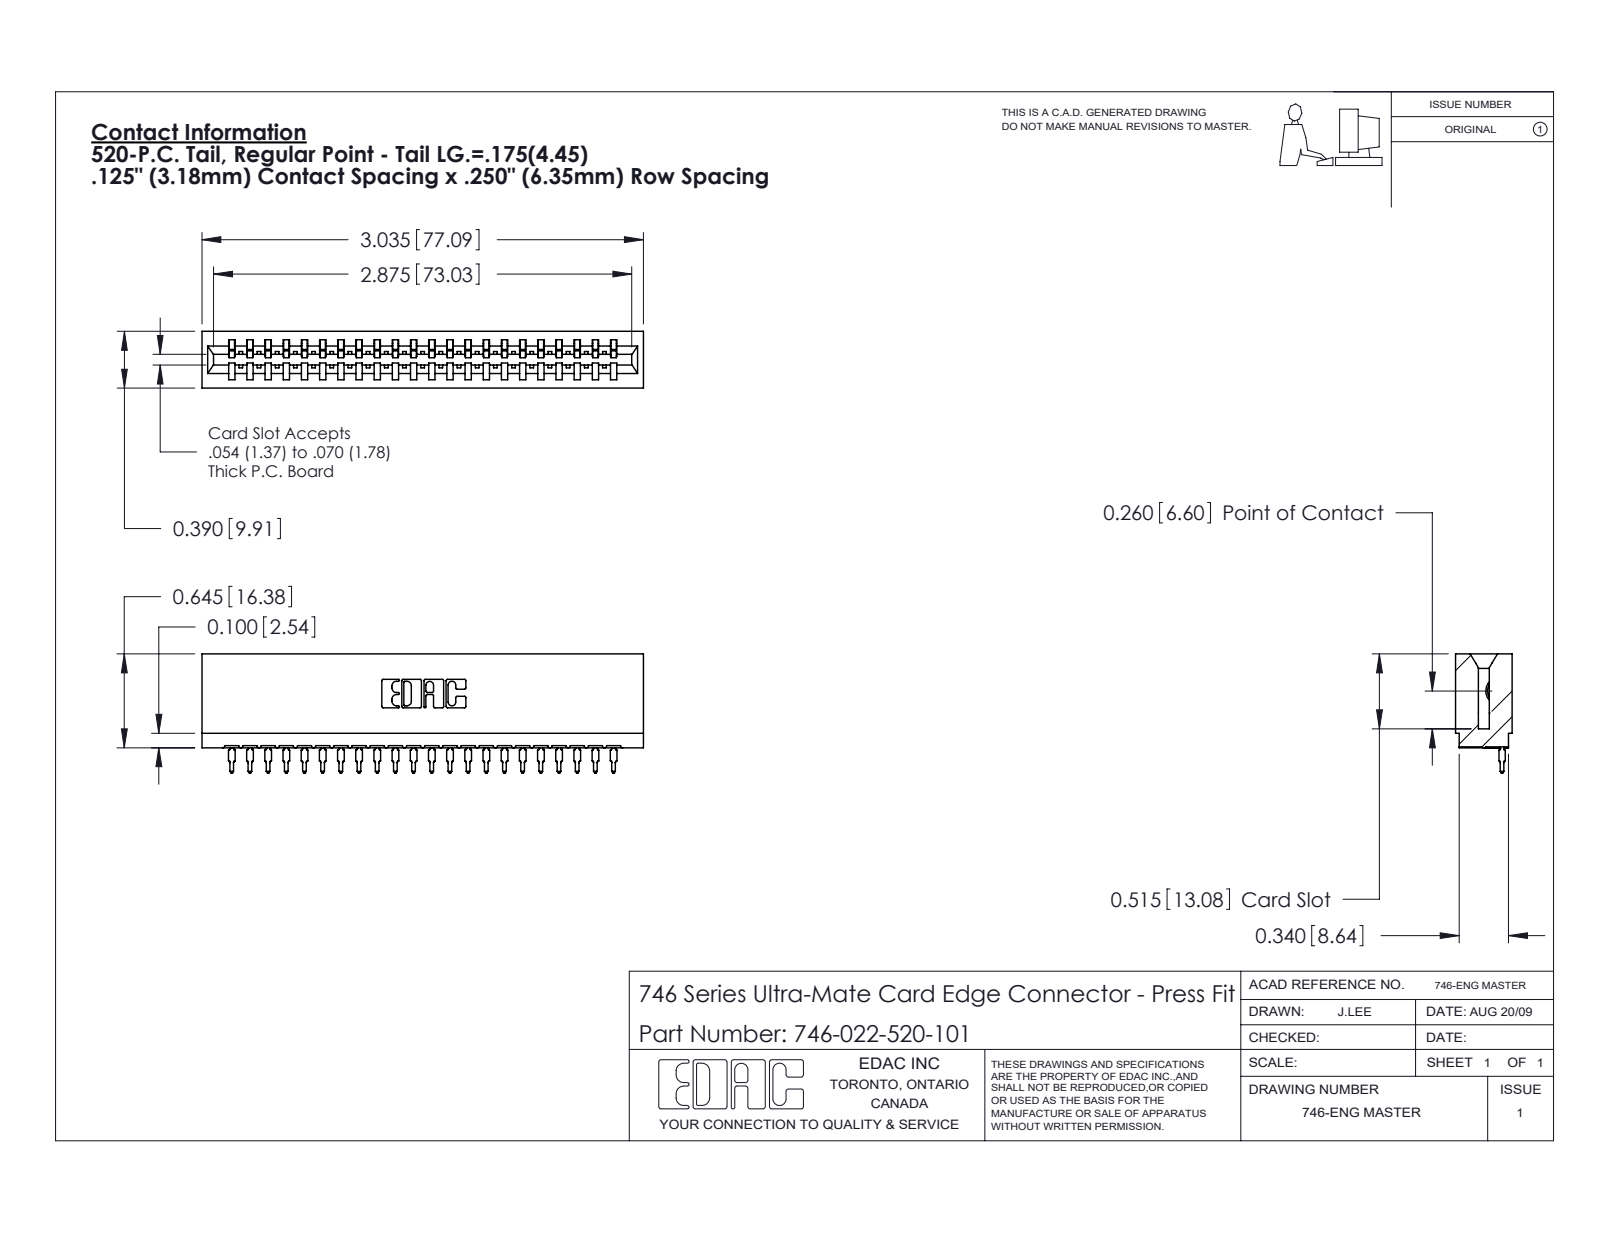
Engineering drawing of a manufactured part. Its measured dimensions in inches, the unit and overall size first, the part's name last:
Units: inches
Overall size (bounding box): 3.035 × 0.819 × 0.39
Partial cylindrical surfaces — rounded edges, fillets, slot ends (radius × count): R0.021 ×44, R0.015 ×23, R0.01 ×22, R0.007 ×6, R0.031 ×6, R0.005 ×4, R0.011 ×4, R0.026 ×3
Main face-to-face distances: 0.057, 0.333, 0.25, 0.39, 0.5, 0.025, 0.307, 0.125, 0.125, 0.375
Volume: 0.498 in³ · Surface area: 17.98 in²
Bodies: 23 solids, 2473 faces (1441 planar, 460 cylindrical, 572 other)
Part name (STEP PRODUCT): 746-022-520-101; 746-292-001_520; 746 Part_.515 Slot Depth - 01
STEP written by: SolidWorks 2020 (CONFIG_CONTROL_DESIGN)
